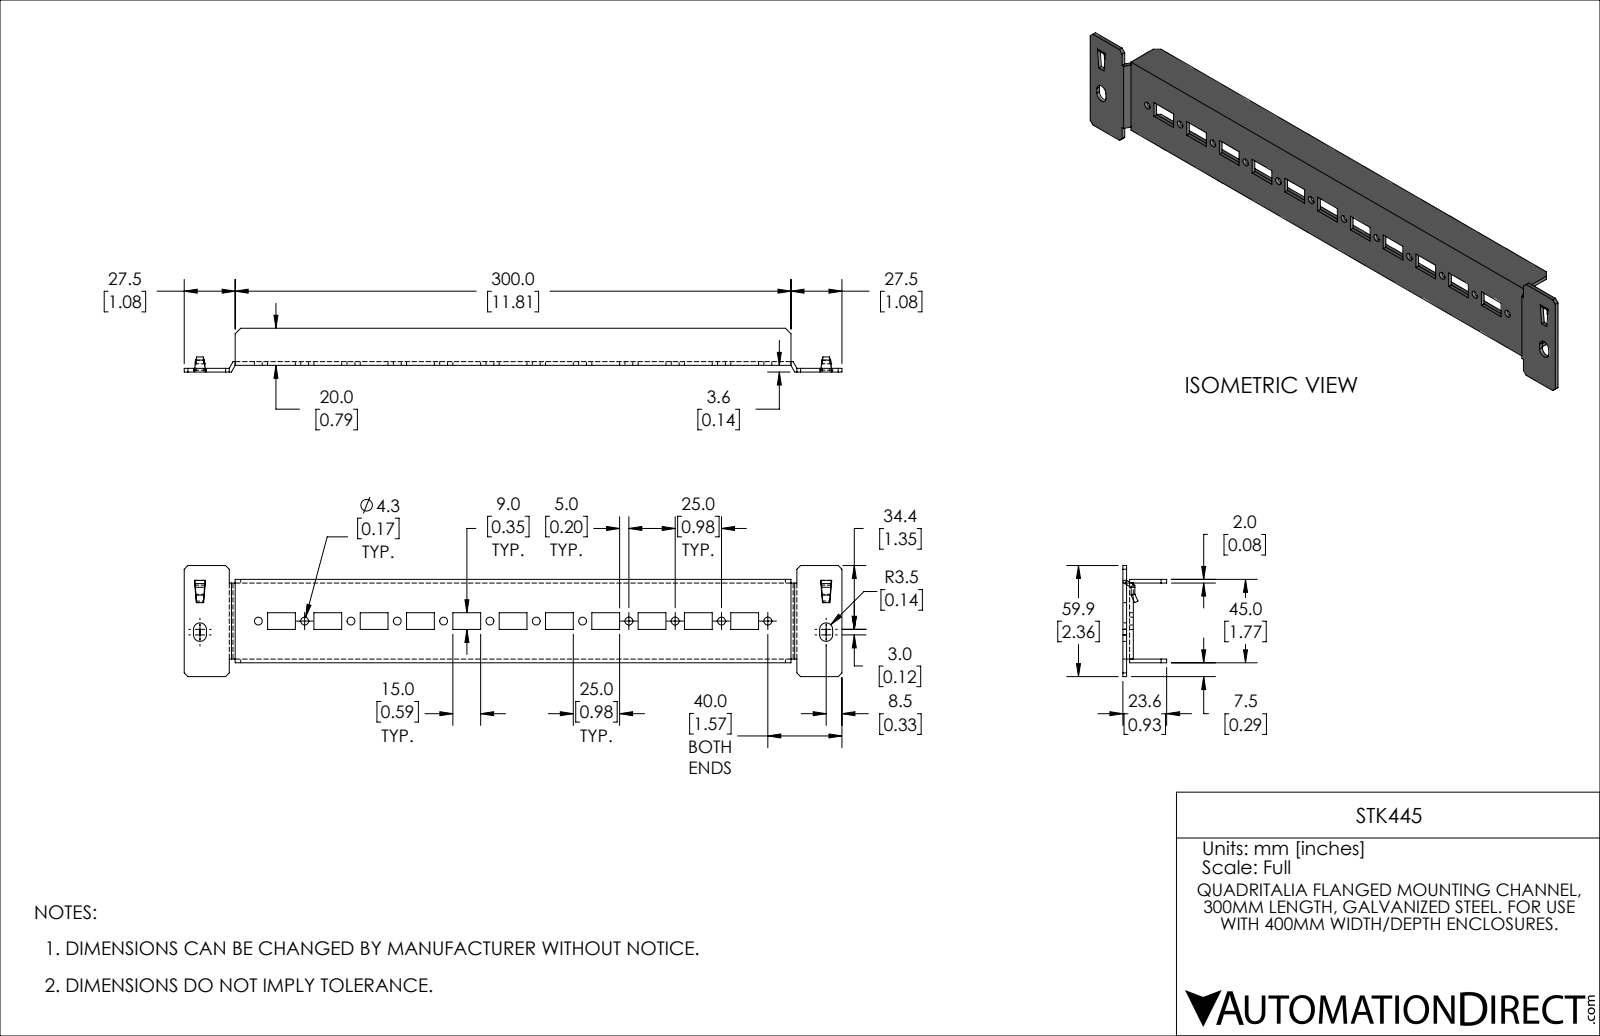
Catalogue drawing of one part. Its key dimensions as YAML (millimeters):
part_name: "STK445"
step_written_by: "SolidWorks 2021 (CONFIG_CONTROL_DESIGN)"
units: millimeters
bodies: {solids: 1, faces: 168, planar: 138, cylindrical: 18, other: 12}
overall_size: [355, 59.9, 23.6]
volume: 51720
surface_area: 55330
round_holes:
  - {diameter: 4.2, count: 12}
partial_cylinders:
  - {radius: 3.5, count: 4}
  - {radius: 2, count: 1}
face_to_face_distances: [2, 43, 45, 3.6, 41, 5.6, 1.6, 18, 20, 23.6]
hole_center_spacings: [25, 50, 75, 100, 125, 150, 175, 200]
